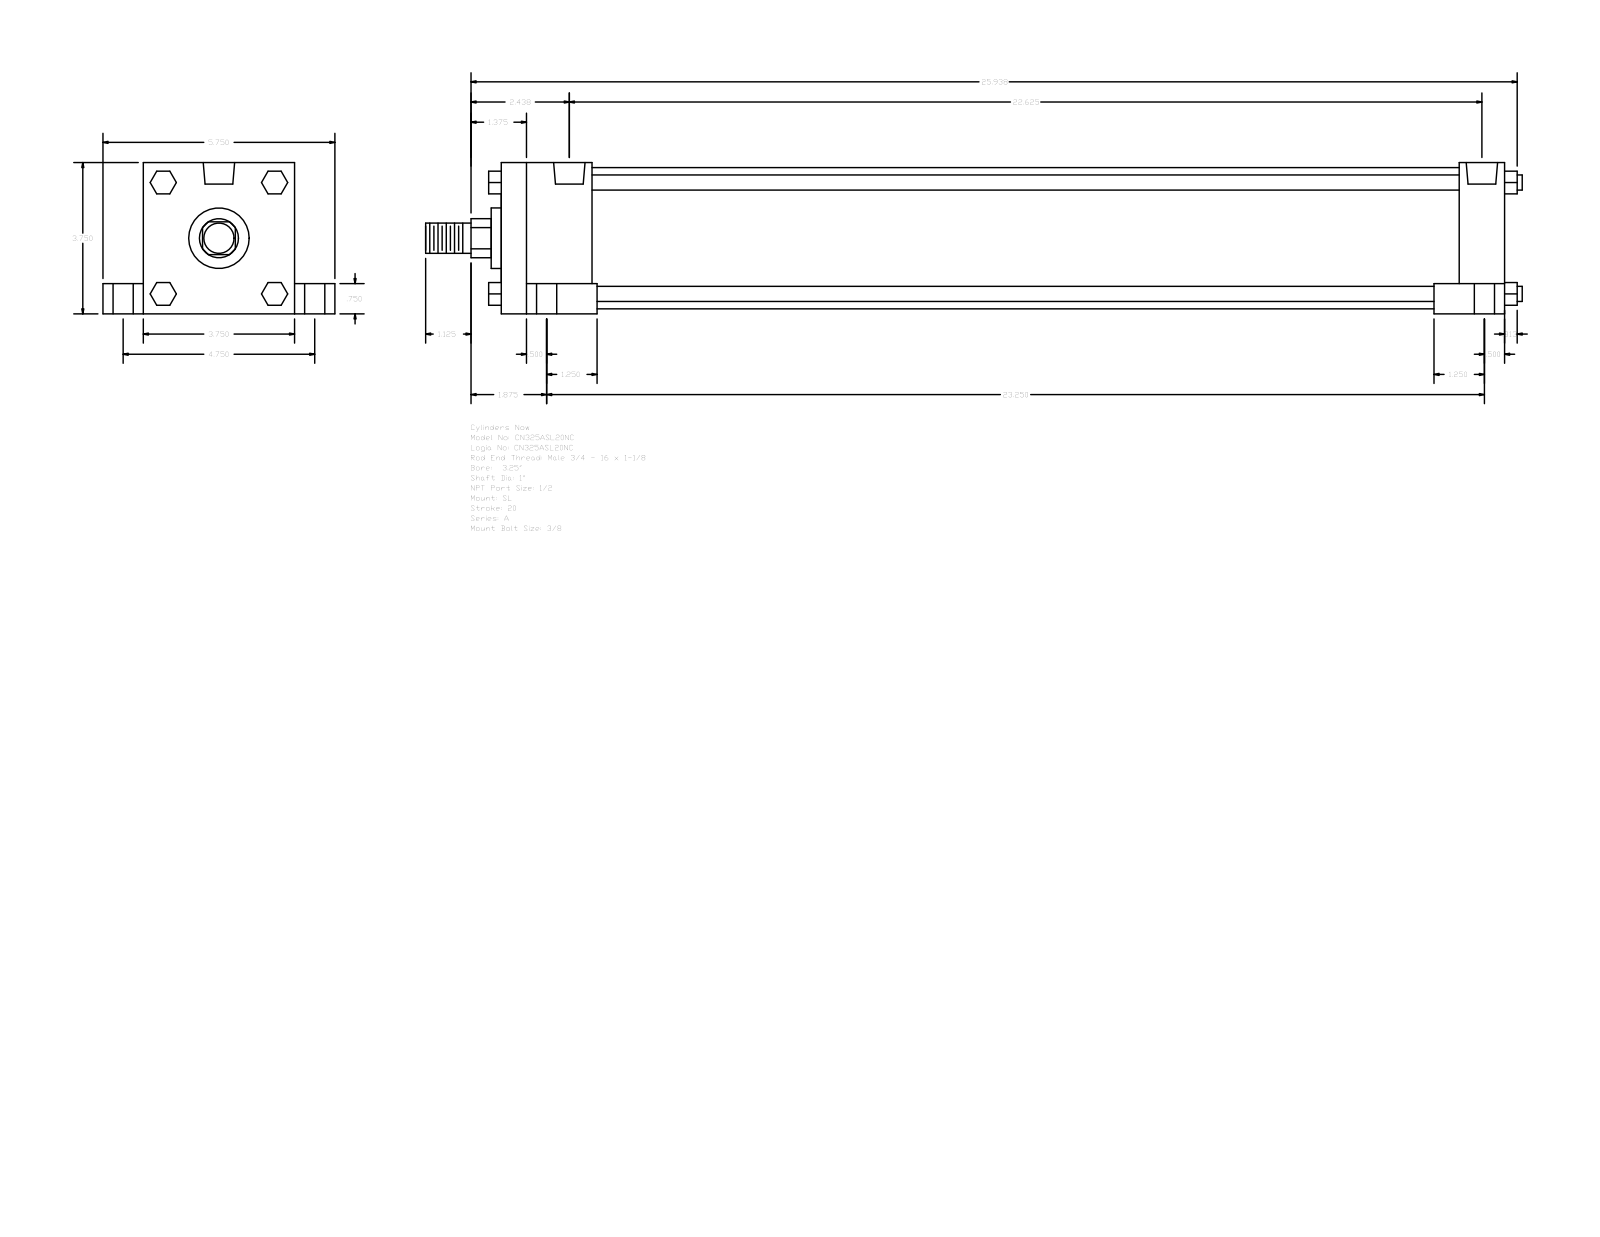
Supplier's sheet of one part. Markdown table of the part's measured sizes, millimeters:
| quantity | value |
| --- | --- |
| part name | A_SL__0325_1 |
| STEP written by | GSSL Pune (CONFIG_CONTROL_DESIGN) |
| units | millimeters |
| bodies | 0 solids, 150 faces (114 planar, 36 cylindrical, 0 other) |
| overall size | 690.56 × 146.05 × 95.25 |
| round holes (diameter × count) | 8.73 × 4, 12.7 × 4, 19.05 × 4, 19.77 × 2 |
| round bosses / shafts (diameter × count) | 9.53 × 4, 88.9 × 1, 38.1 × 1, 25.4 × 1, 19.05 × 1 |
| partial cylindrical surfaces (radius × count) | 12.29 × 1 |
| main face-to-face distances | 95.24, 631.83, 19.05, 25.41, 120.65, 76.19, 57.15, 603.25, 546.1, 574.68 |
| hole center spacings | 3.18, 60.35, 60.52, 62, 62.81, 120.66, 568.32, 571.5 |
